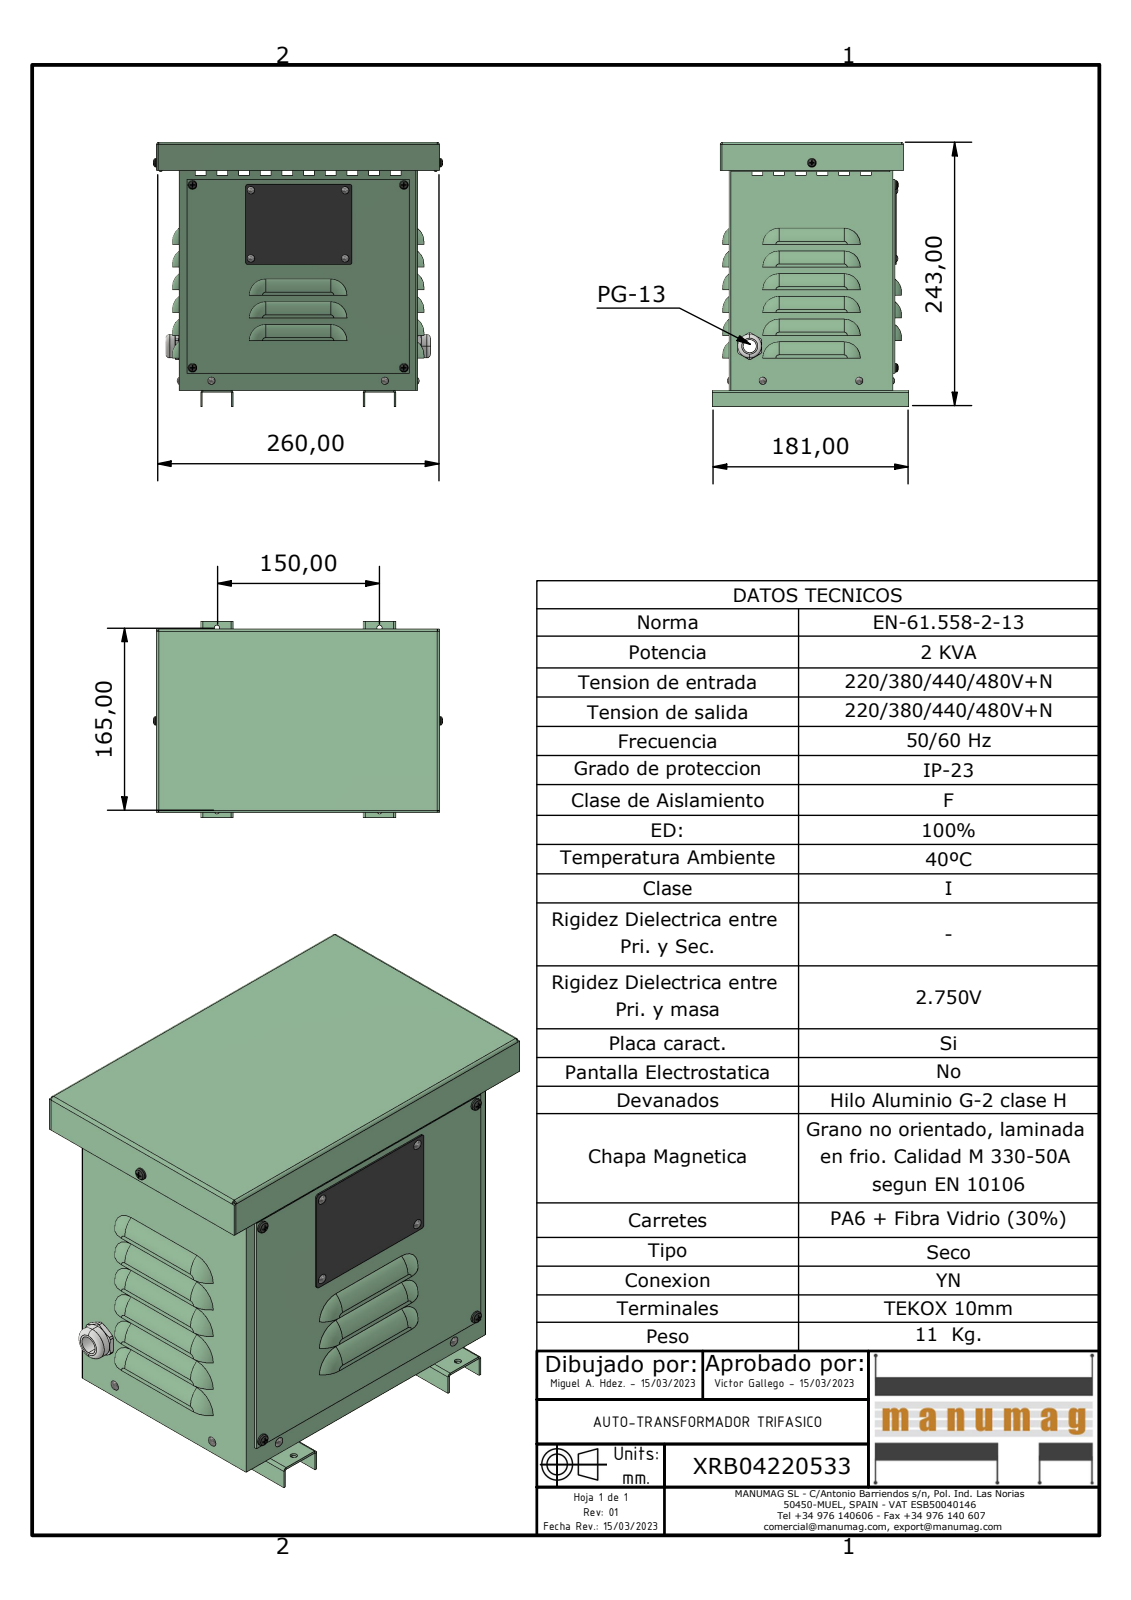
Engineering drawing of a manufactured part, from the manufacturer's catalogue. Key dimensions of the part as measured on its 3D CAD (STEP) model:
Part name (STEP PRODUCT): XRB04220533; JE001 - JE002 EXPORT CUERPO; JE001 - JE002 EXPORT BASE; JE001 - JE002 EXPORT PATA (+6 more)
STEP written by: Autodesk Inventor 2023 (AUTOMOTIVE_DESIGN)
Units: millimetres
Bodies: 27 solids, 1168 faces (639 planar, 259 cylindrical, 270 other)
Overall size (bounding box): 267.13 × 244.49 × 181
Volume: 601 317 mm³ · Surface area: 669 713 mm²
Round holes (diameter × count): ⌀4.8 ×13, ⌀3.8 ×5, ⌀3 ×4, ⌀4 ×4, ⌀12 ×1, ⌀22 ×1
Round bosses / shafts (diameter × count): ⌀3.2 ×8, ⌀4 ×5, ⌀3.62 ×5, ⌀21.7 ×1, ⌀20.4 ×1, ⌀20.3 ×1, ⌀18.95 ×1
Partial cylindrical surfaces — rounded edges, fillets, slot ends (radius × count): R14 ×24, R15 ×21, R4 ×18, R1.5 ×13, R2 ×12, R0.5 ×8, R2.5 ×8, R14.5 ×6
Main face-to-face distances: 1.5, 149.5, 227.99, 218.5, 229.49, 151.5, 151, 2, 153, 217
Hole centre spacings: 169, 150, 21.22, 26, 43.01, 50, 54.23, 63
